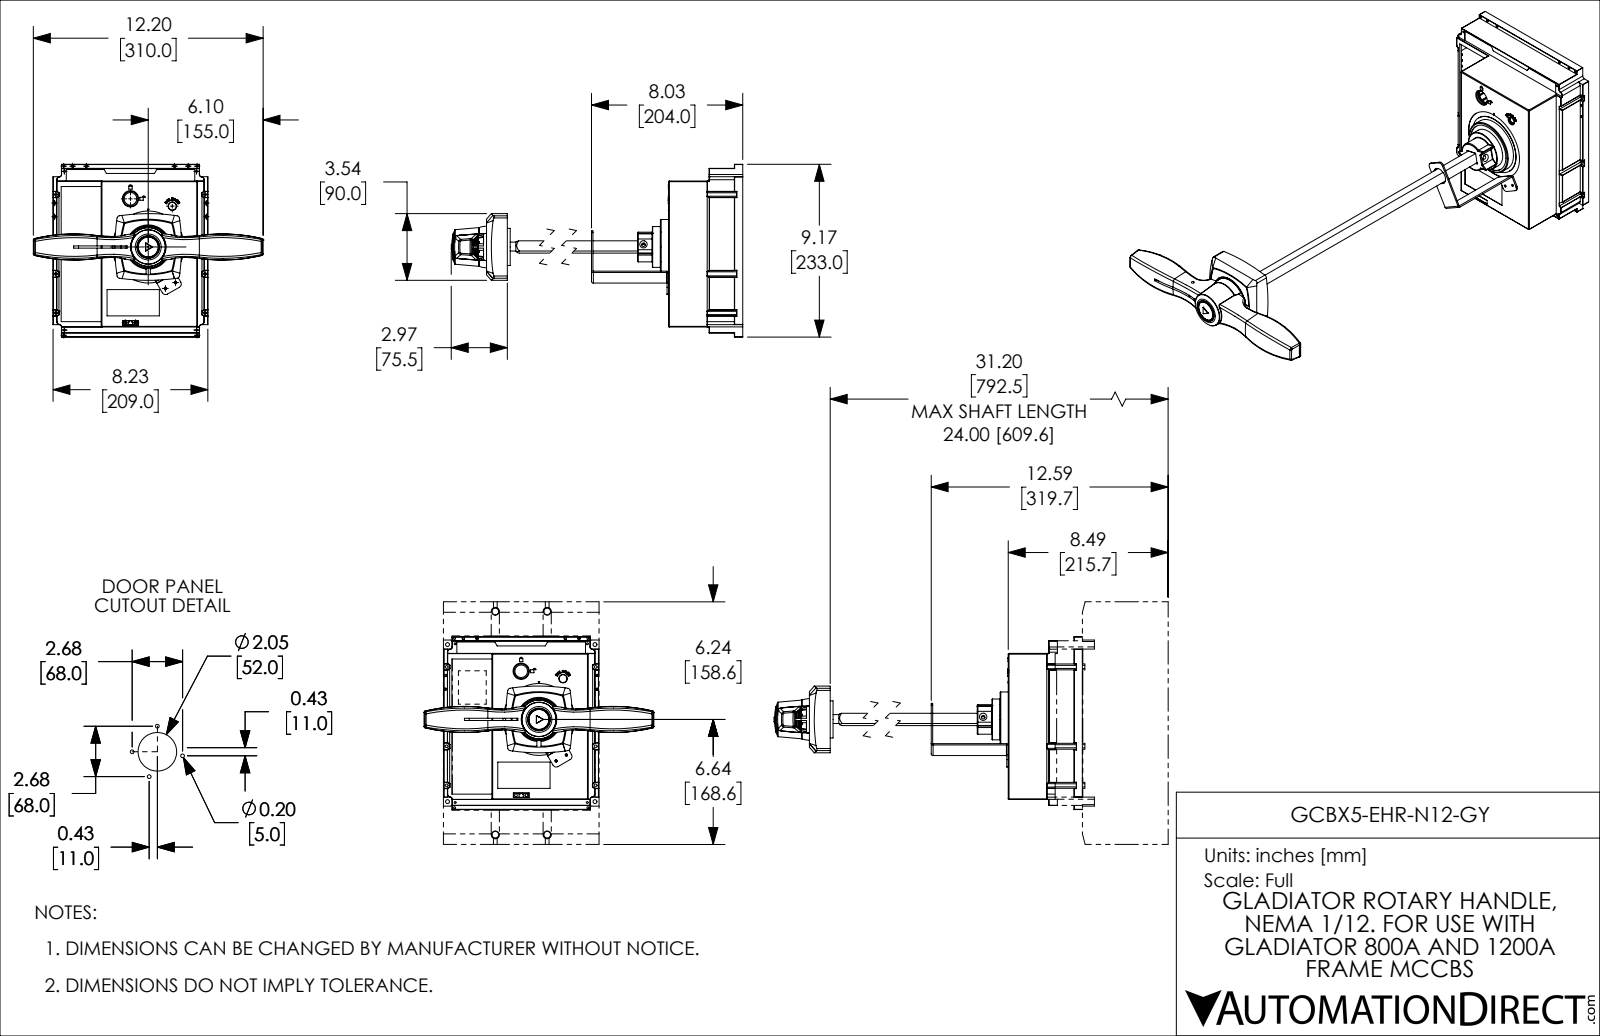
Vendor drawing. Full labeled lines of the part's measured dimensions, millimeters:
Part name (STEP PRODUCT): GCBX5-EHR-N12-GY
STEP written by: SolidWorks 2021 (CONFIG_CONTROL_DESIGN)
Units: millimetres
Bodies: 6 solids, 2788 faces (1858 planar, 518 cylindrical, 412 other)
Overall size (bounding box): 652 × 310 × 233
Volume: 873 460 mm³ · Surface area: 468 725 mm²
Round holes (diameter × count): ⌀2.6 ×18, ⌀3.8 ×8, ⌀5 ×7, ⌀8 ×4, ⌀3 ×2, ⌀3.2 ×2, ⌀4.3 ×2, ⌀4 ×1, ⌀7.1 ×1, ⌀10 ×1, ⌀10.5 ×1, ⌀17 ×1
Round bosses / shafts (diameter × count): ⌀6 ×2, ⌀83 ×1, ⌀74 ×1, ⌀73 ×1, ⌀59.5 ×1, ⌀56 ×1, ⌀55 ×1, ⌀50 ×1
Partial cylindrical surfaces — rounded edges, fillets, slot ends (radius × count): R0.3 ×81, R0.5 ×56, R1 ×25, R2 ×14, R2.5 ×10, R3 ×8, R6 ×8, R3.7 ×6
Main face-to-face distances: 3, 8, 2.5, 187, 17, 194, 202, 9, 211, 14.01
Hole centre spacings: 7.05, 18.5, 179.34, 221, 284.52, 198.23, 201, 11.64
